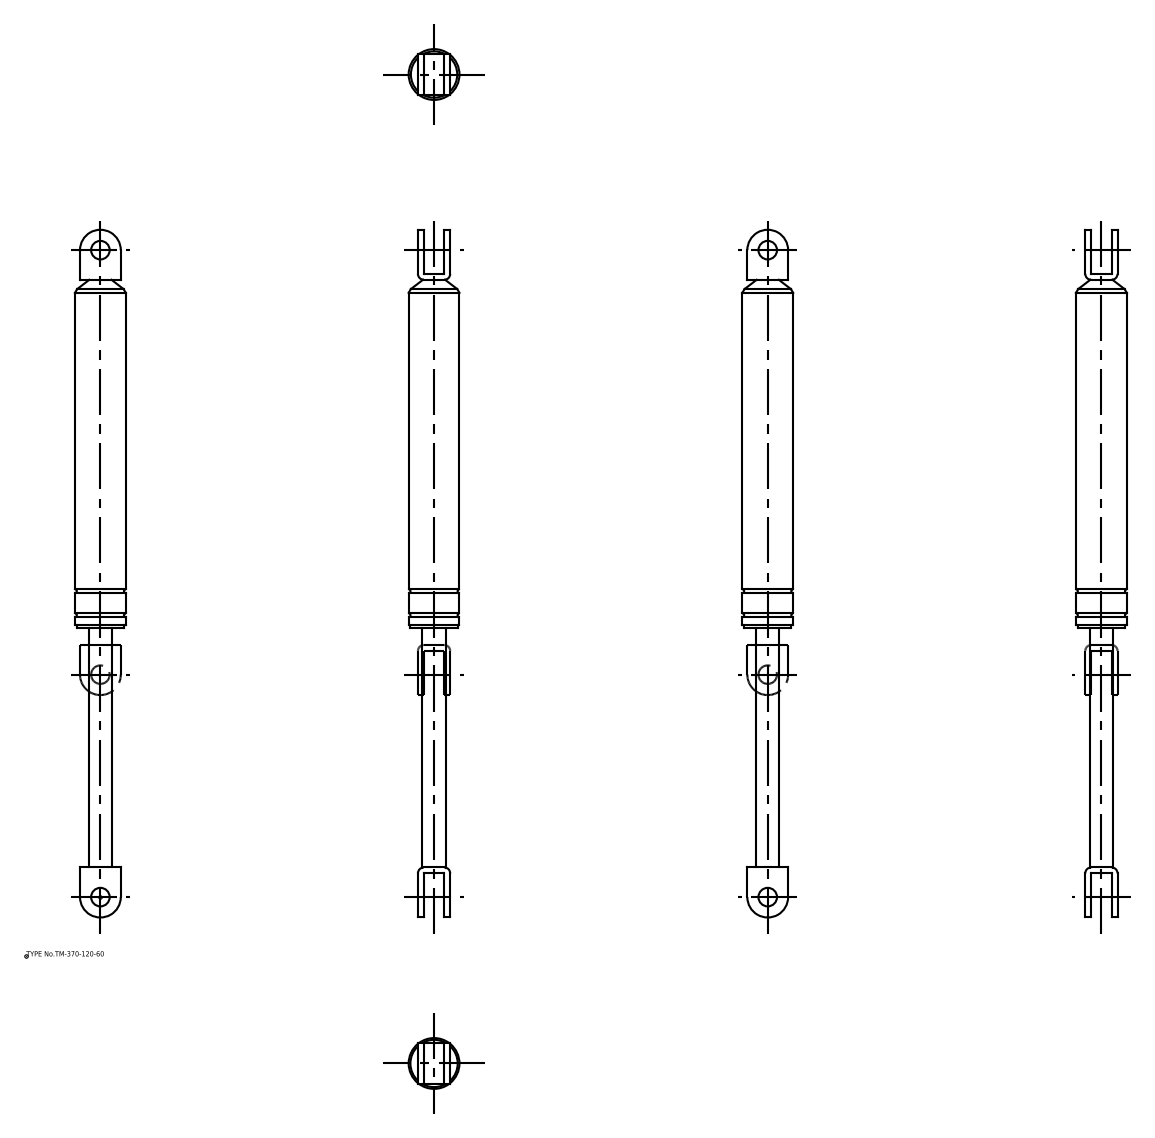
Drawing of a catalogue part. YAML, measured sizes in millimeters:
part_name: "TM_370_120_60; TM_370_120_60_div"
step_written_by: "spGate 16.7.1 (AUTOMOTIVE_DESIGN)"
units: millimeters
bodies: {solids: 2, faces: 64, planar: 22, cylindrical: 32, other: 10}
overall_size: [371, 28.2, 28.2]
volume: 132373
surface_area: 28030
round_holes:
  - {diameter: 10, count: 2}
round_bosses_or_shafts:
  - {diameter: 28.2, count: 1}
  - {diameter: 27.4, count: 1}
  - {diameter: 25.5, count: 1}
  - {diameter: 12.5, count: 1}
partial_cylinders:
  - {radius: 3.2, count: 4}
  - {radius: 11, count: 2}
face_to_face_distances: [3.2, 14.2, 17.4, 11, 22, 320.2, 132.2, 323.4, 191.2, 188]
hole_center_spacings: [349]
